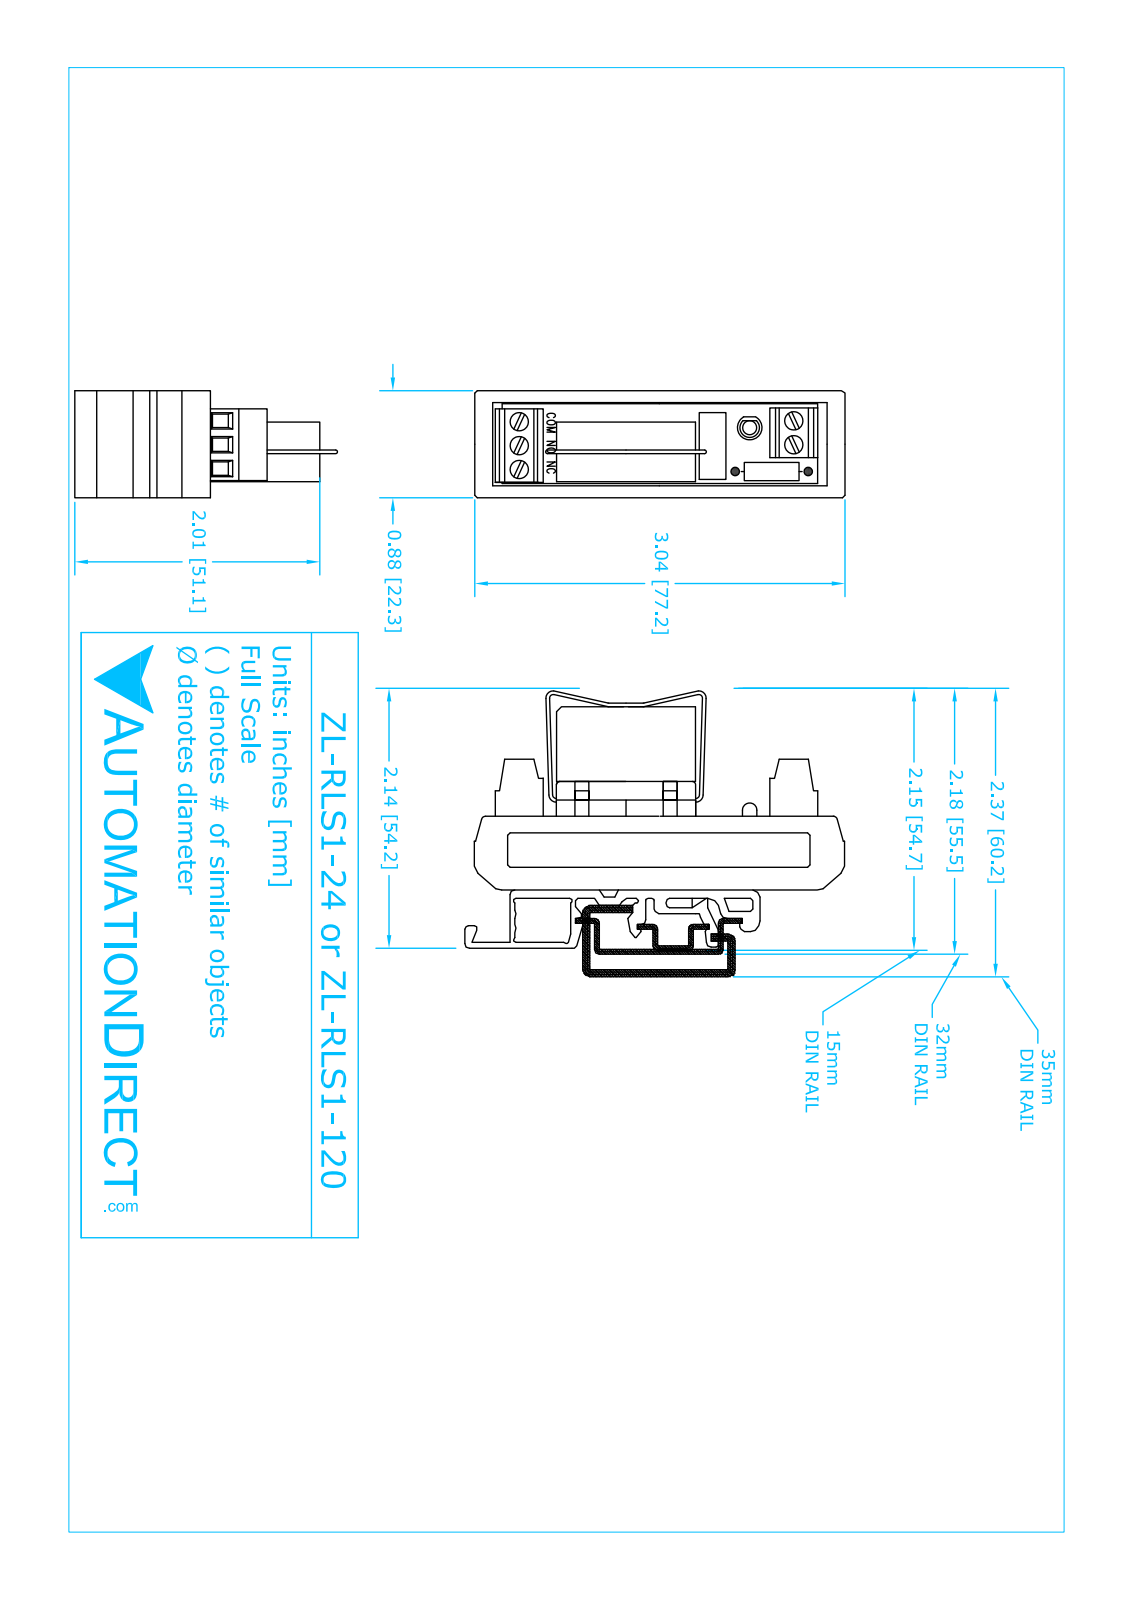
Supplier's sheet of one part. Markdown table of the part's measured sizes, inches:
| quantity | value |
| --- | --- |
| part name | ZL-RLS1-120 |
| STEP written by | SolidWorks 2014 (AUTOMOTIVE_DESIGN) |
| units | inches |
| bodies | 3 solids, 295 faces (203 planar, 54 cylindrical, 38 other) |
| overall size | 3.04 × 2.183 × 0.88 |
| volume | 2.704 in³ |
| surface area | 27.93 in² |
| round holes (diameter × count) | 0.15 × 4, 0.149 × 1 |
| round bosses / shafts (diameter × count) | 0.15 × 1 |
| partial cylindrical surfaces (radius × count) | 0.015 × 28, 0.025 × 2, 0.025 × 2, 0.03 × 2 |
| main face-to-face distances | 0.88, 0.65, 0.02, 0.652, 0.976, 0.018, 0.67, 0.42, 1.07, 0.4 |
| hole center spacings | 0.2, 2.237, 0.215, 0.4, 2.245, 2.246, 2.248, 2.273 |
